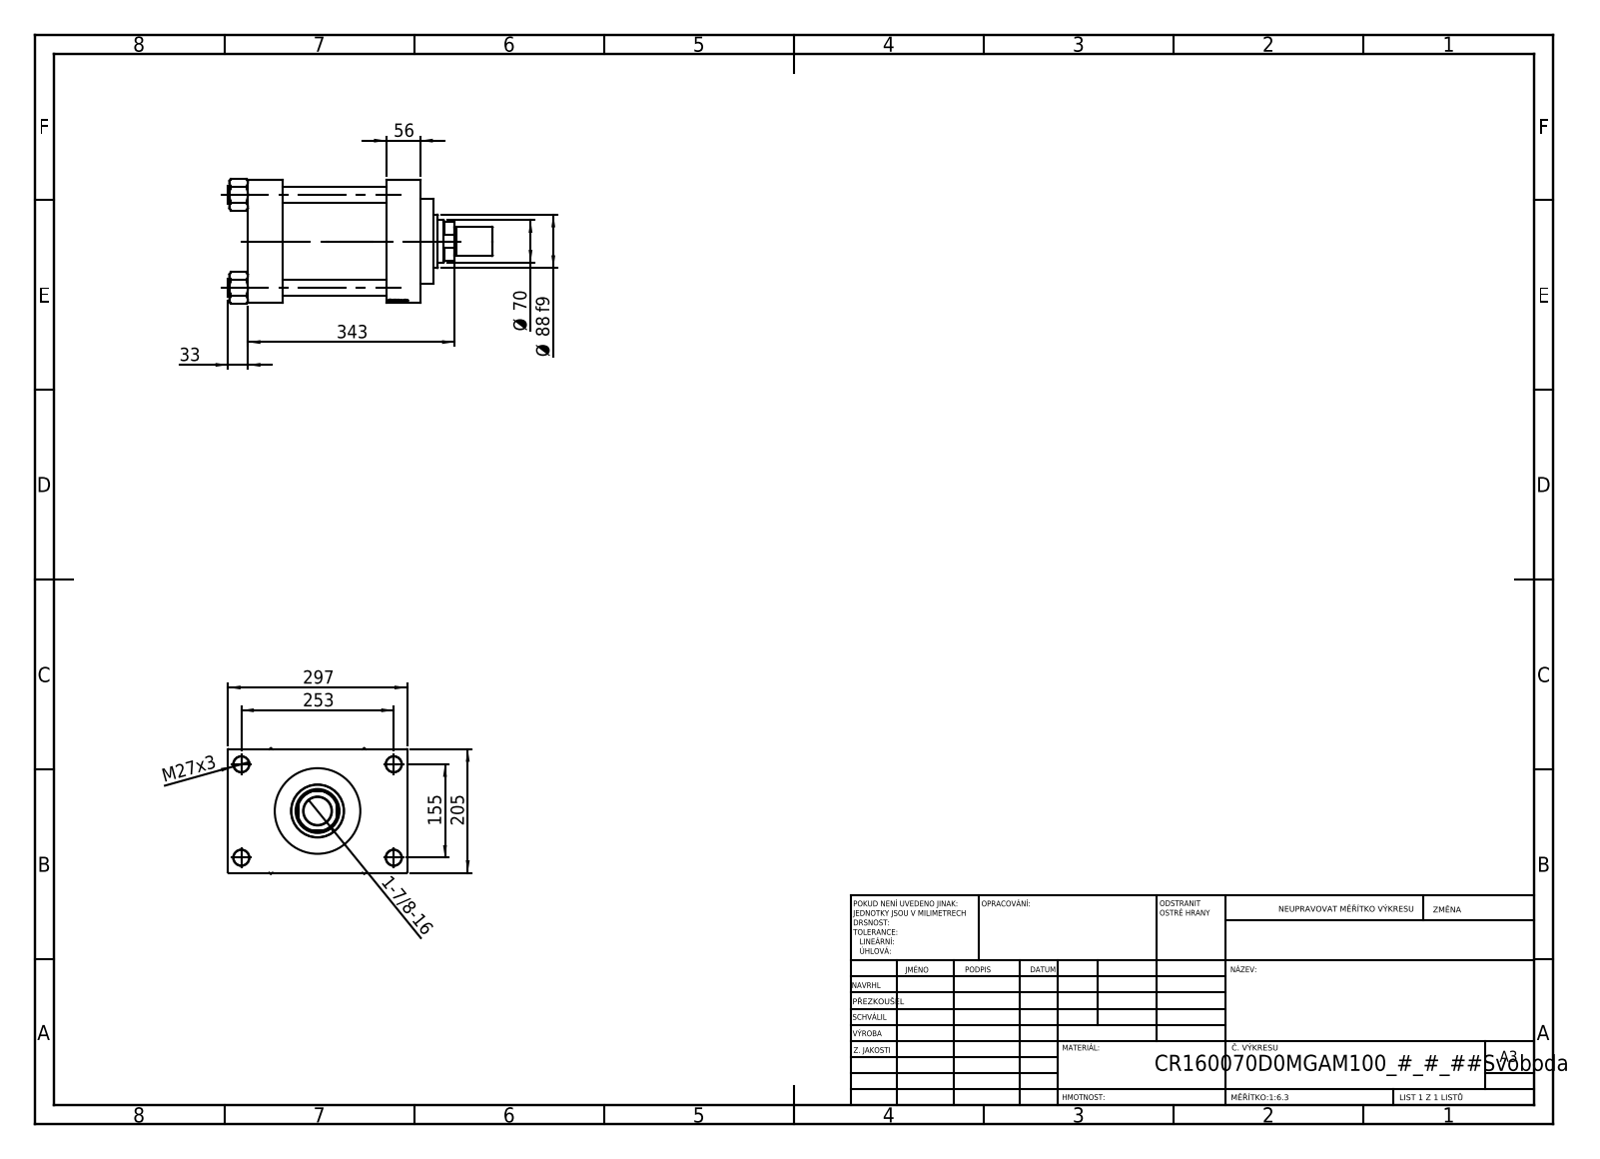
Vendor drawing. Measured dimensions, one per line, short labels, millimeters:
name: NUT_M5_D; V215CR_VCP_D; V215CR_D_Body; ROD_END_AH (+2 more)
written by: SolidWorks 2019 (CONFIG_CONTROL_DESIGN)
unit: mm
bodies: 12 solids, 1163 faces (548 planar, 91 cylindrical, 524 other)
size: 439 × 297 × 208.14
volume: 8 623 000 mm³; area: 864 898 mm²
holes: 4× ⌀26, 4× ⌀27, 2× ⌀7, 2× ⌀33.24, 2× ⌀45, 1× ⌀46.5, 1× ⌀70, 1× ⌀73, 1× ⌀120, 1× ⌀142, 1× ⌀160
bosses: 4× ⌀30, 1× ⌀166, 1× ⌀88, 1× ⌀48, 1× ⌀46
rounds: 1× R34
face distances: 58, 230, 172, 286, 228, 56, 205, 46, 251, 100
hole spacings: 49.05, 109.53, 148.35, 154.9, 162.53, 203.95, 256.13, 155
